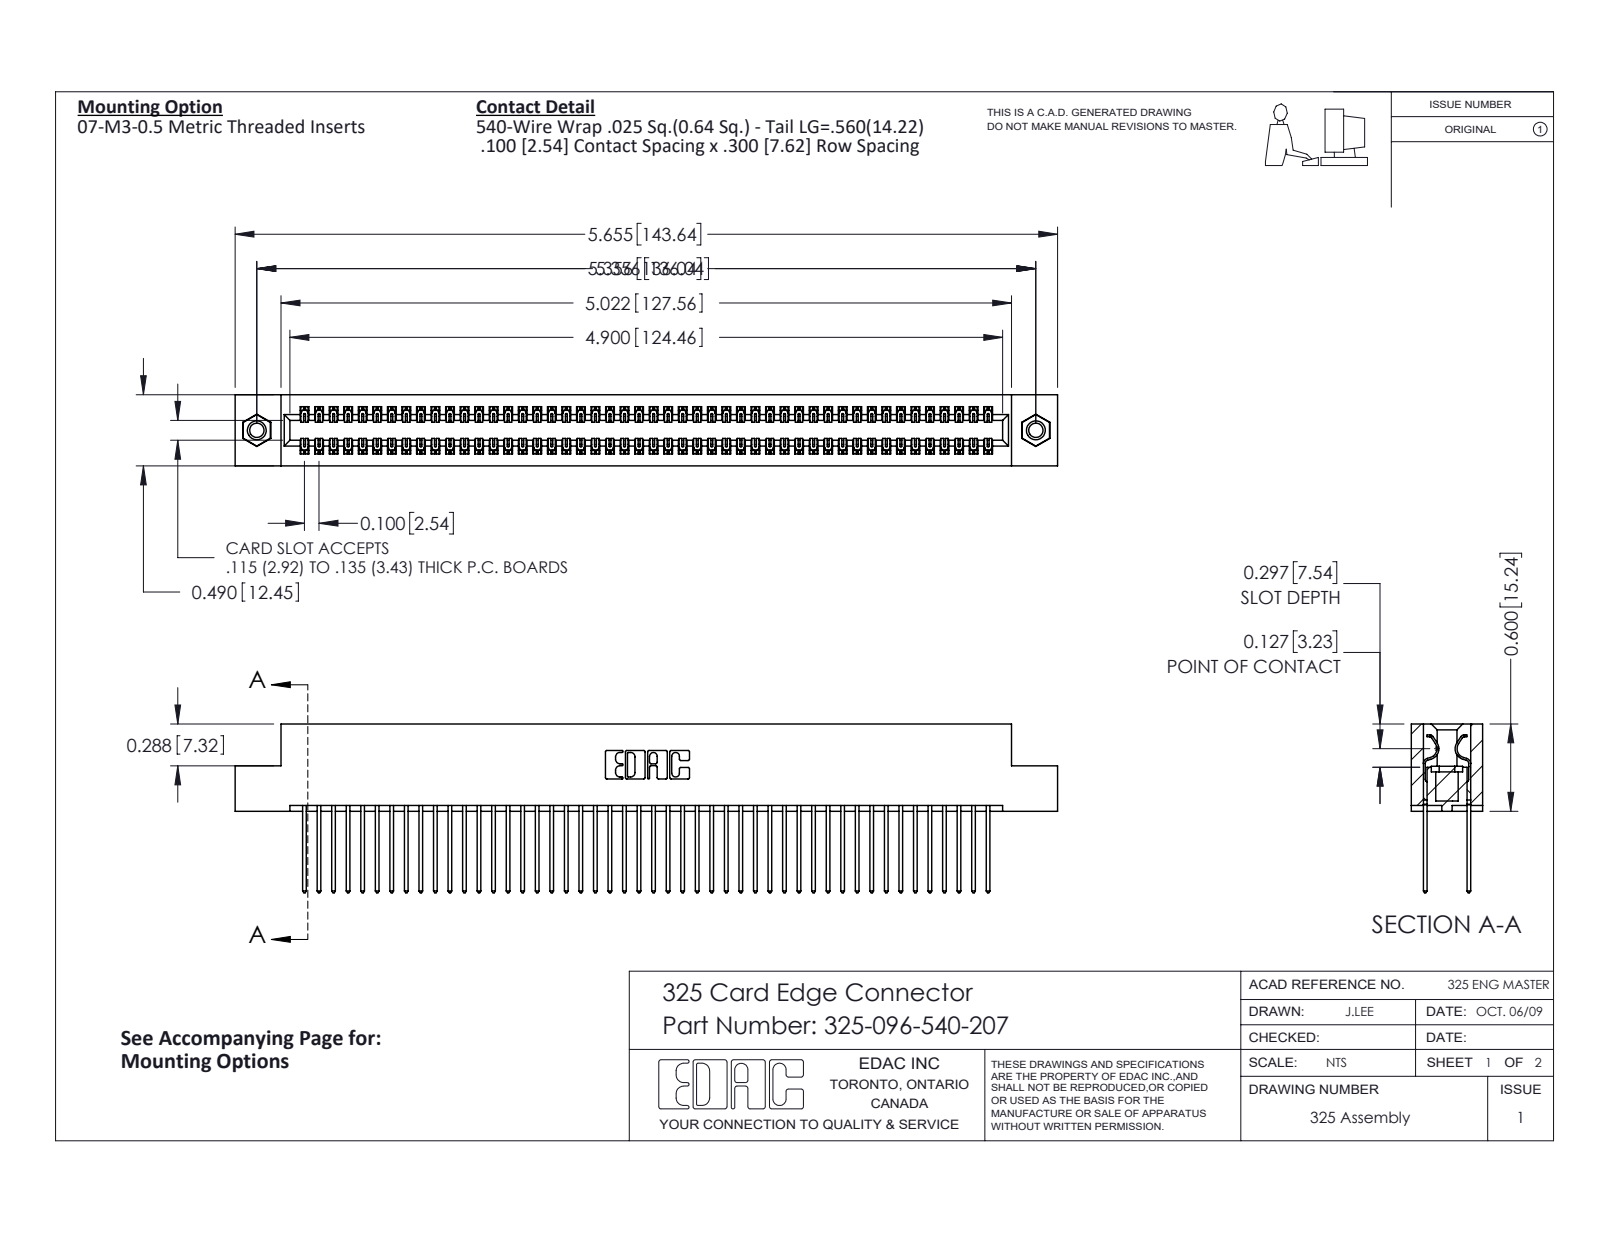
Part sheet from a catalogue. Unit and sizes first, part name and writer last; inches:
Units: inches
Overall size (bounding box): 5.655 × 1.16 × 0.49
Round holes (diameter × count): ⌀0.098 ×2, ⌀0.125 ×2, ⌀0.16 ×2
Round bosses / shafts (diameter × count): ⌀0.155 ×2
Partial cylindrical surfaces — rounded edges, fillets, slot ends (radius × count): R0.006 ×144, R0.01 ×96, R0.01 ×22, R0.007 ×6, R0.031 ×6, R0.026 ×3, R0.014 ×2, R0.022 ×2
Main face-to-face distances: 0.083, 0.407, 0.3, 0.107, 0.383, 0.025, 0.325, 0.49, 0.275, 0.56
Hole centre spacings: 5.356
Volume: 1.156 in³ · Surface area: 38.49 in²
Bodies: 99 solids, 5166 faces (3558 planar, 1592 cylindrical, 16 other)
Part name (STEP PRODUCT): 325 Part_TI; 325-096-540-207; 325-292-001_325-293-140; 345-250-001_345-250-005-103
STEP written by: SolidWorks 2016 (CONFIG_CONTROL_DESIGN)
